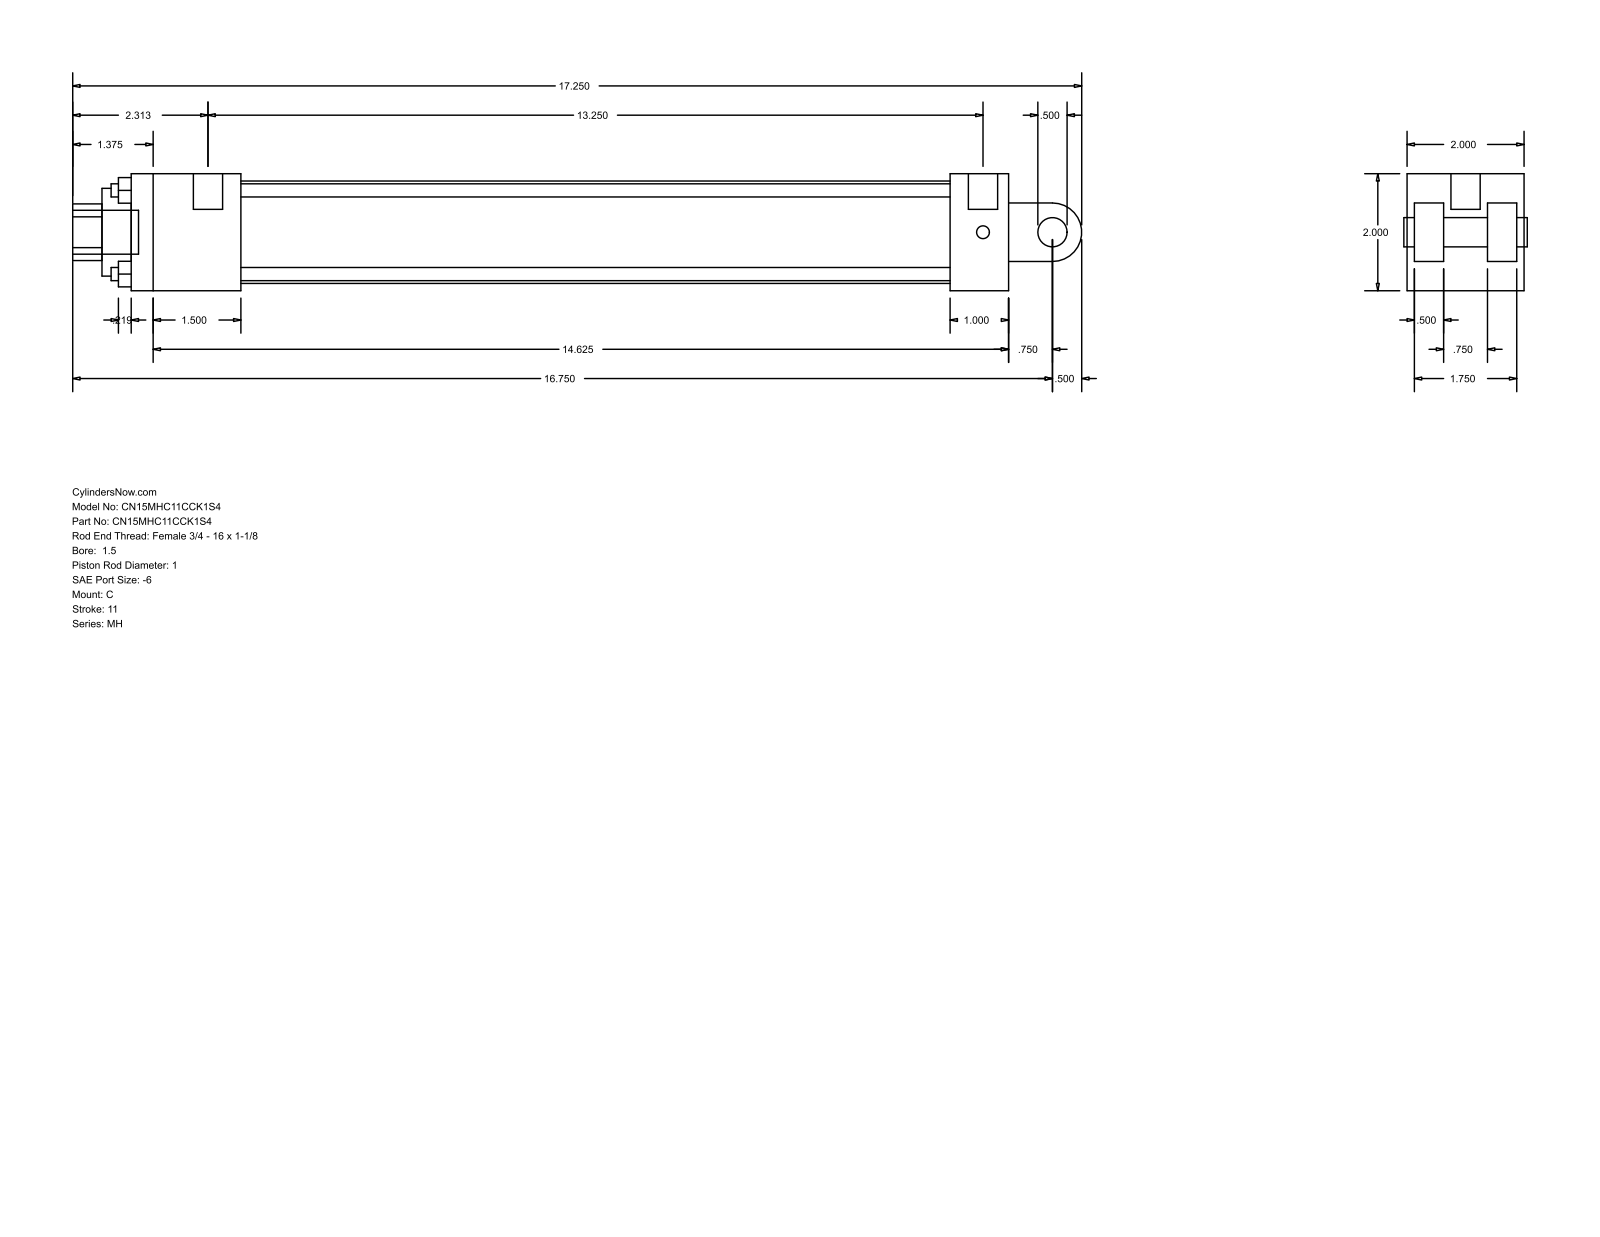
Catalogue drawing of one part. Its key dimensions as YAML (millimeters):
part_name: "MH_C__0150_1"
step_written_by: "GSSL Pune (CONFIG_CONTROL_DESIGN)"
units: millimeters
bodies: {solids: 0, faces: 99, planar: 70, cylindrical: 29, other: 0}
overall_size: [438.15, 50.8, 50.8]
round_holes:
  - {diameter: 5.71, count: 4}
  - {diameter: 5.56, count: 2}
  - {diameter: 12.7, count: 1}
  - {diameter: 25.4, count: 1}
  - {diameter: 38.1, count: 1}
  - {diameter: 44.45, count: 1}
round_bosses_or_shafts:
  - {diameter: 12.7, count: 2}
  - {diameter: 5.56, count: 2}
  - {diameter: 19.05, count: 1}
partial_cylinders:
  - {radius: 12.29, count: 1}
  - {radius: 12.7, count: 1}
face_to_face_distances: [50.8, 12.7, 47.63, 3.17, 15.87, 25.4, 34.93, 31.76, 381, 38.1]
hole_center_spacings: [25.68, 36.32, 51.36]
